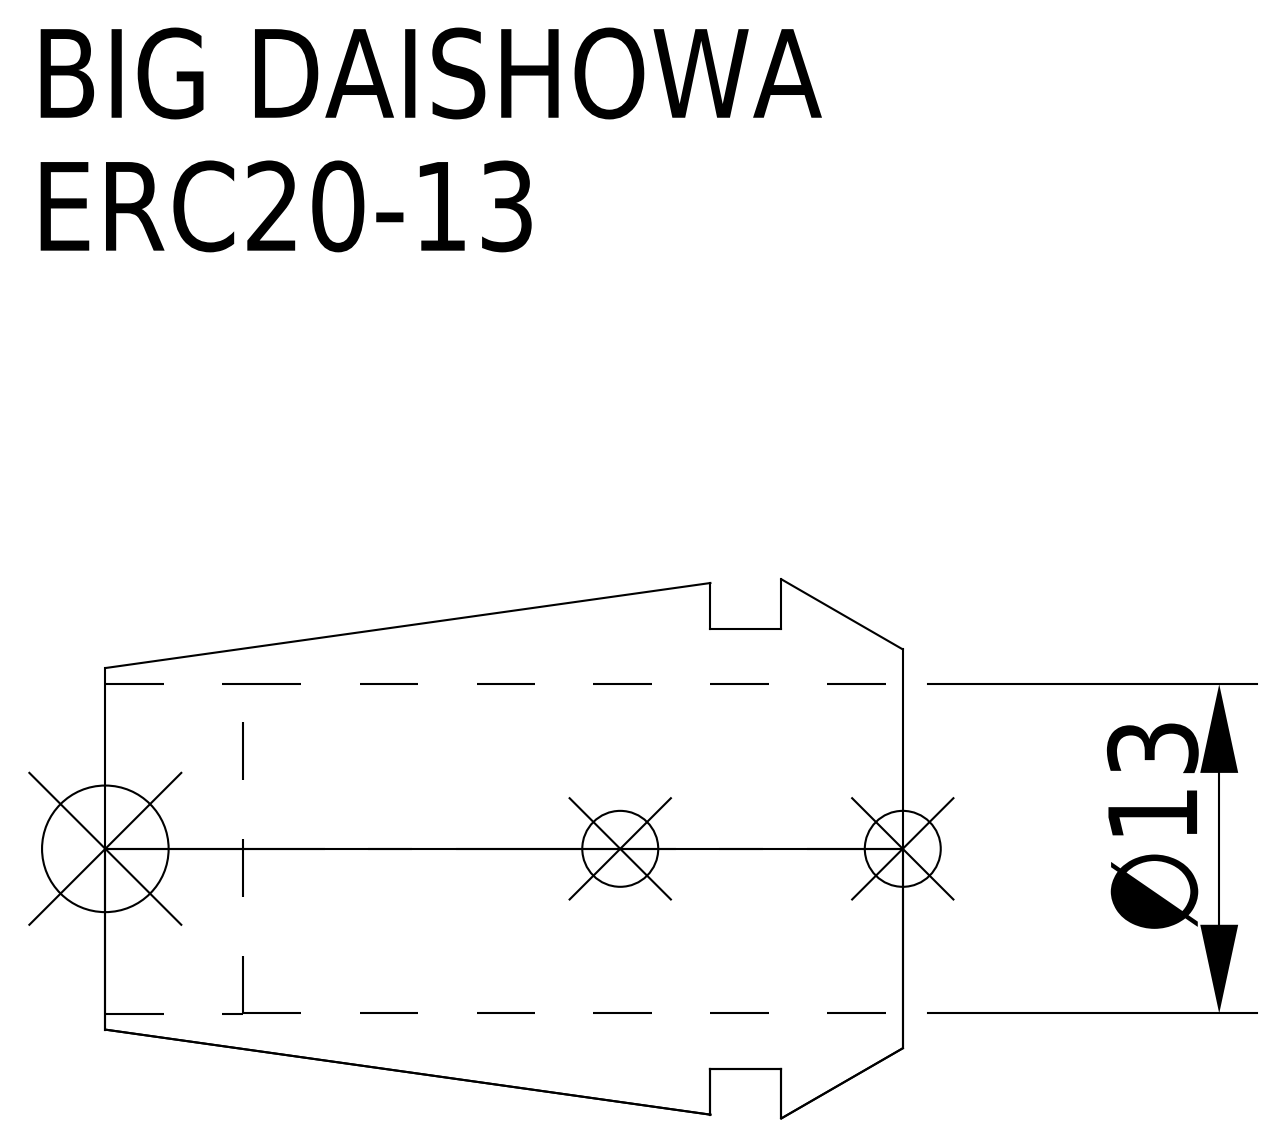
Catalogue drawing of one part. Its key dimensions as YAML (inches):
part_name: "ERC20-13"
step_written_by: "CREO PARAMETRIC BY PTC INC, 2016380 (AUTOMOTIVE_DESIGN)"
units: inches
bodies: {solids: 1, faces: 15, planar: 5, cylindrical: 6, other: 4}
overall_size: [1.24, 0.839, 0.839]
volume: 0.226
surface_area: 5.298
round_holes:
  - {diameter: 0.512, count: 1}
  - {diameter: 0.514, count: 1}
round_bosses_or_shafts:
  - {diameter: 0.685, count: 1}
face_to_face_distances: [0.11, 0.189, 0.299, 1.24, 1.051, 0.941, 1.027, 0.838, 0.728, 0.213]
